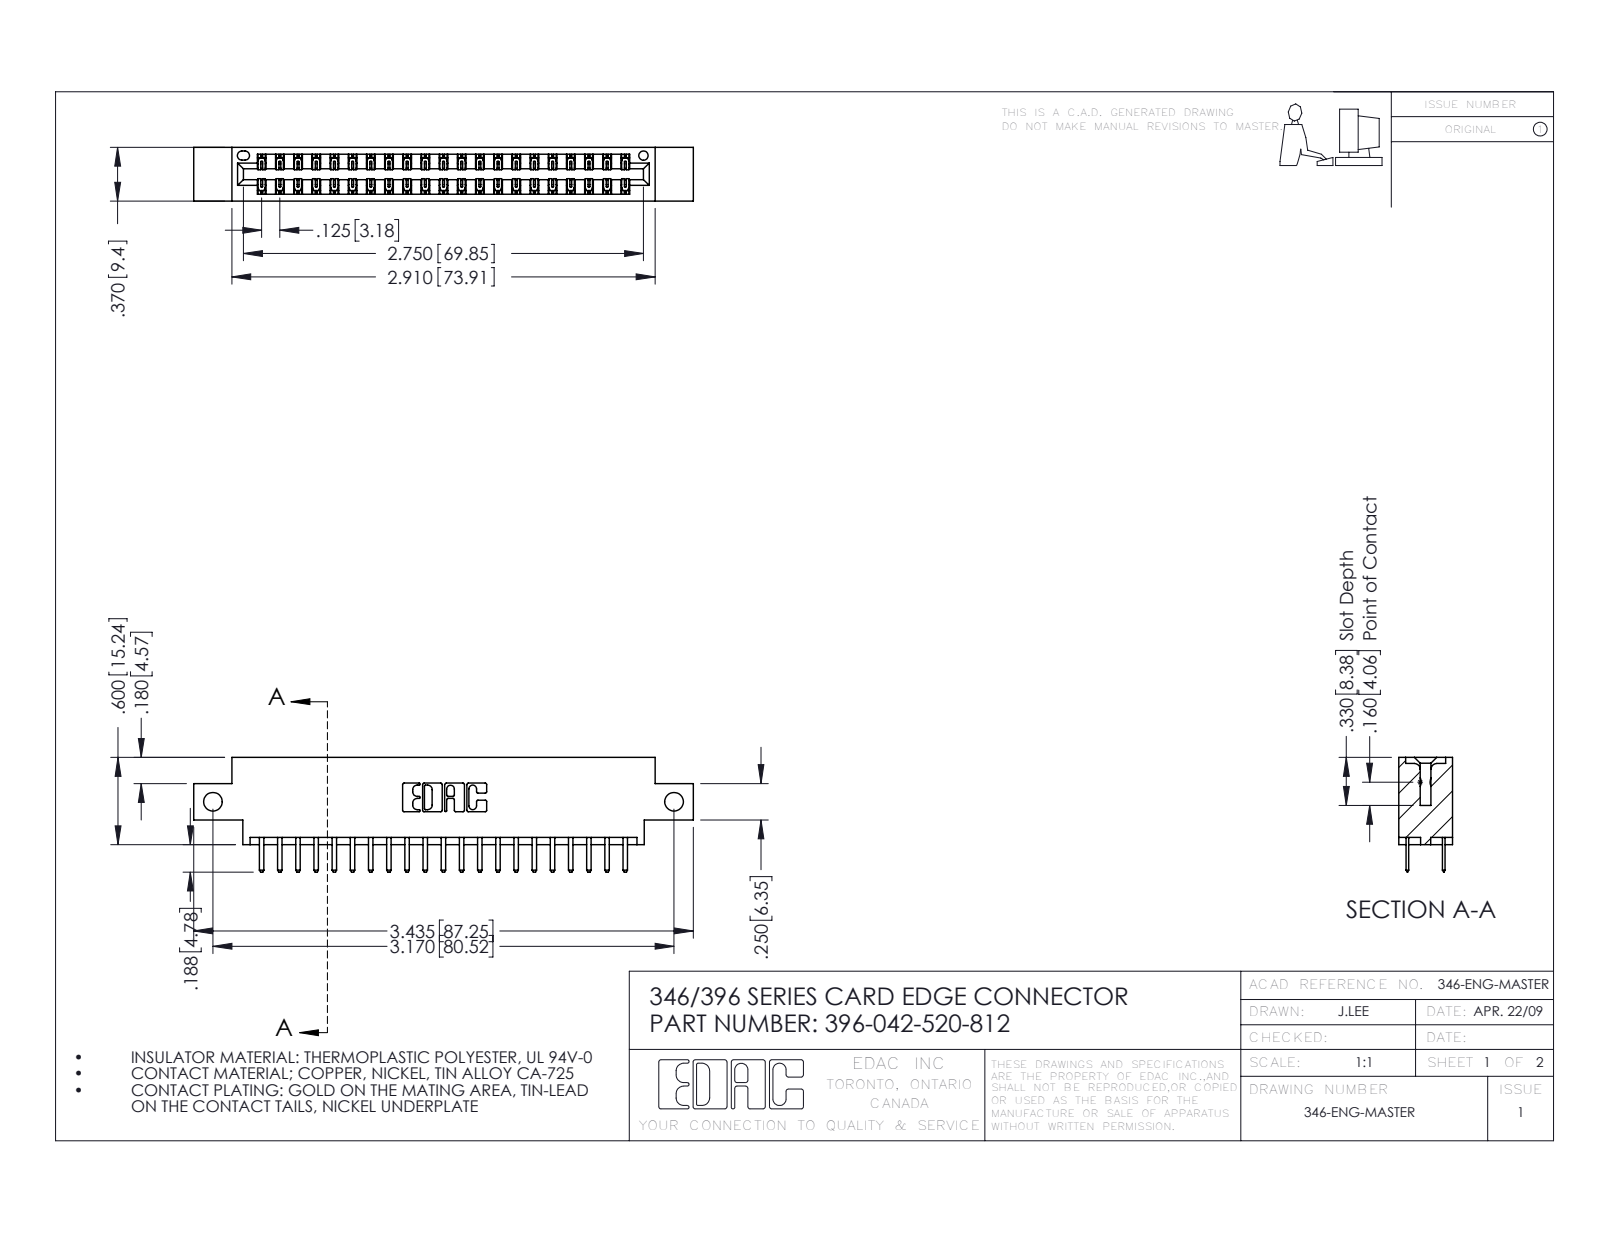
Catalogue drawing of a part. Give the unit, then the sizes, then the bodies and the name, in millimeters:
Units: millimetres
Overall size (bounding box): 87.2 × 20 × 9.4
Round holes (diameter × count): ⌀3.3 ×2, ⌀1.6 ×1
Partial cylindrical surfaces — rounded edges, fillets, slot ends (radius × count): R0.2 ×63, R0.3 ×46, R0.3 ×22, R0.2 ×6, R0.8 ×6, R0.7 ×3, R0.4 ×2, R0.6 ×2
Main face-to-face distances: 1.2, 8.2, 6.4, 9.4, 7, 1.8, 7.6, 0.6, 3.8, 5.6
Hole centre spacings: 80.5
Volume: 8 080 mm³ · Surface area: 10 780 mm²
Bodies: 43 solids, 2478 faces (1634 planar, 844 cylindrical, 0 other)
Part name (STEP PRODUCT): 345-292-001_345-293-120; 396-042-520-812; 346 Part_0.170 Offset - Side Mount
STEP written by: SolidWorks 2016 (CONFIG_CONTROL_DESIGN)
